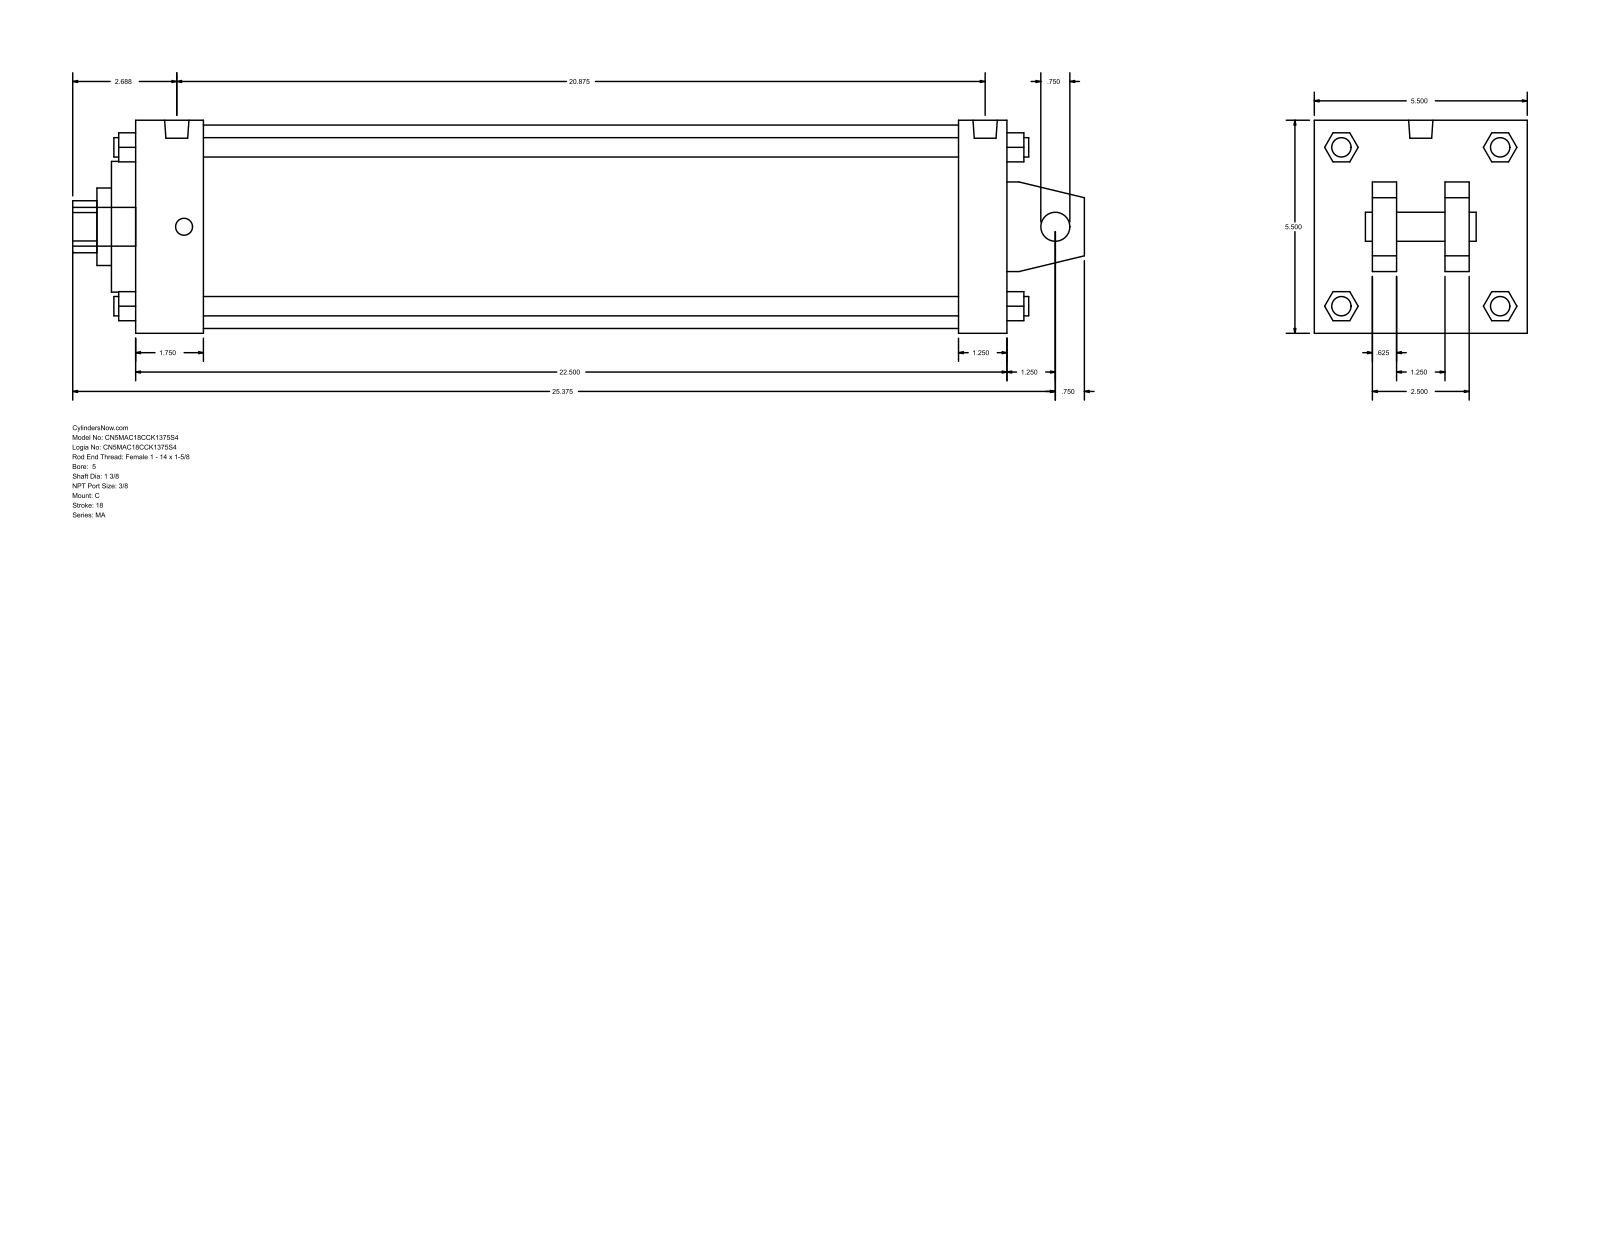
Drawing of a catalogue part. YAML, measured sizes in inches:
part_name: "MA_C__0500_1.375"
step_written_by: "GSSL Pune (CONFIG_CONTROL_DESIGN)"
units: inches
bodies: {solids: 0, faces: 141, planar: 109, cylindrical: 32, other: 0}
overall_size: [26.125, 5.5, 5.5]
round_holes:
  - {diameter: 0.75, count: 1}
  - {diameter: 1.375, count: 1}
  - {diameter: 2, count: 1}
  - {diameter: 3.375, count: 1}
  - {diameter: 5.25, count: 1}
round_bosses_or_shafts:
  - {diameter: 0.5, count: 4}
  - {diameter: 0.437, count: 4}
  - {diameter: 0.627, count: 2}
  - {diameter: 1, count: 1}
partial_cylinders:
  - {radius: 0.672, count: 1}
face_to_face_distances: [5.5, 22.5, 0.625, 21.25, 1.25, 1.75, 19.5, 20.75, 1.5, 4]
